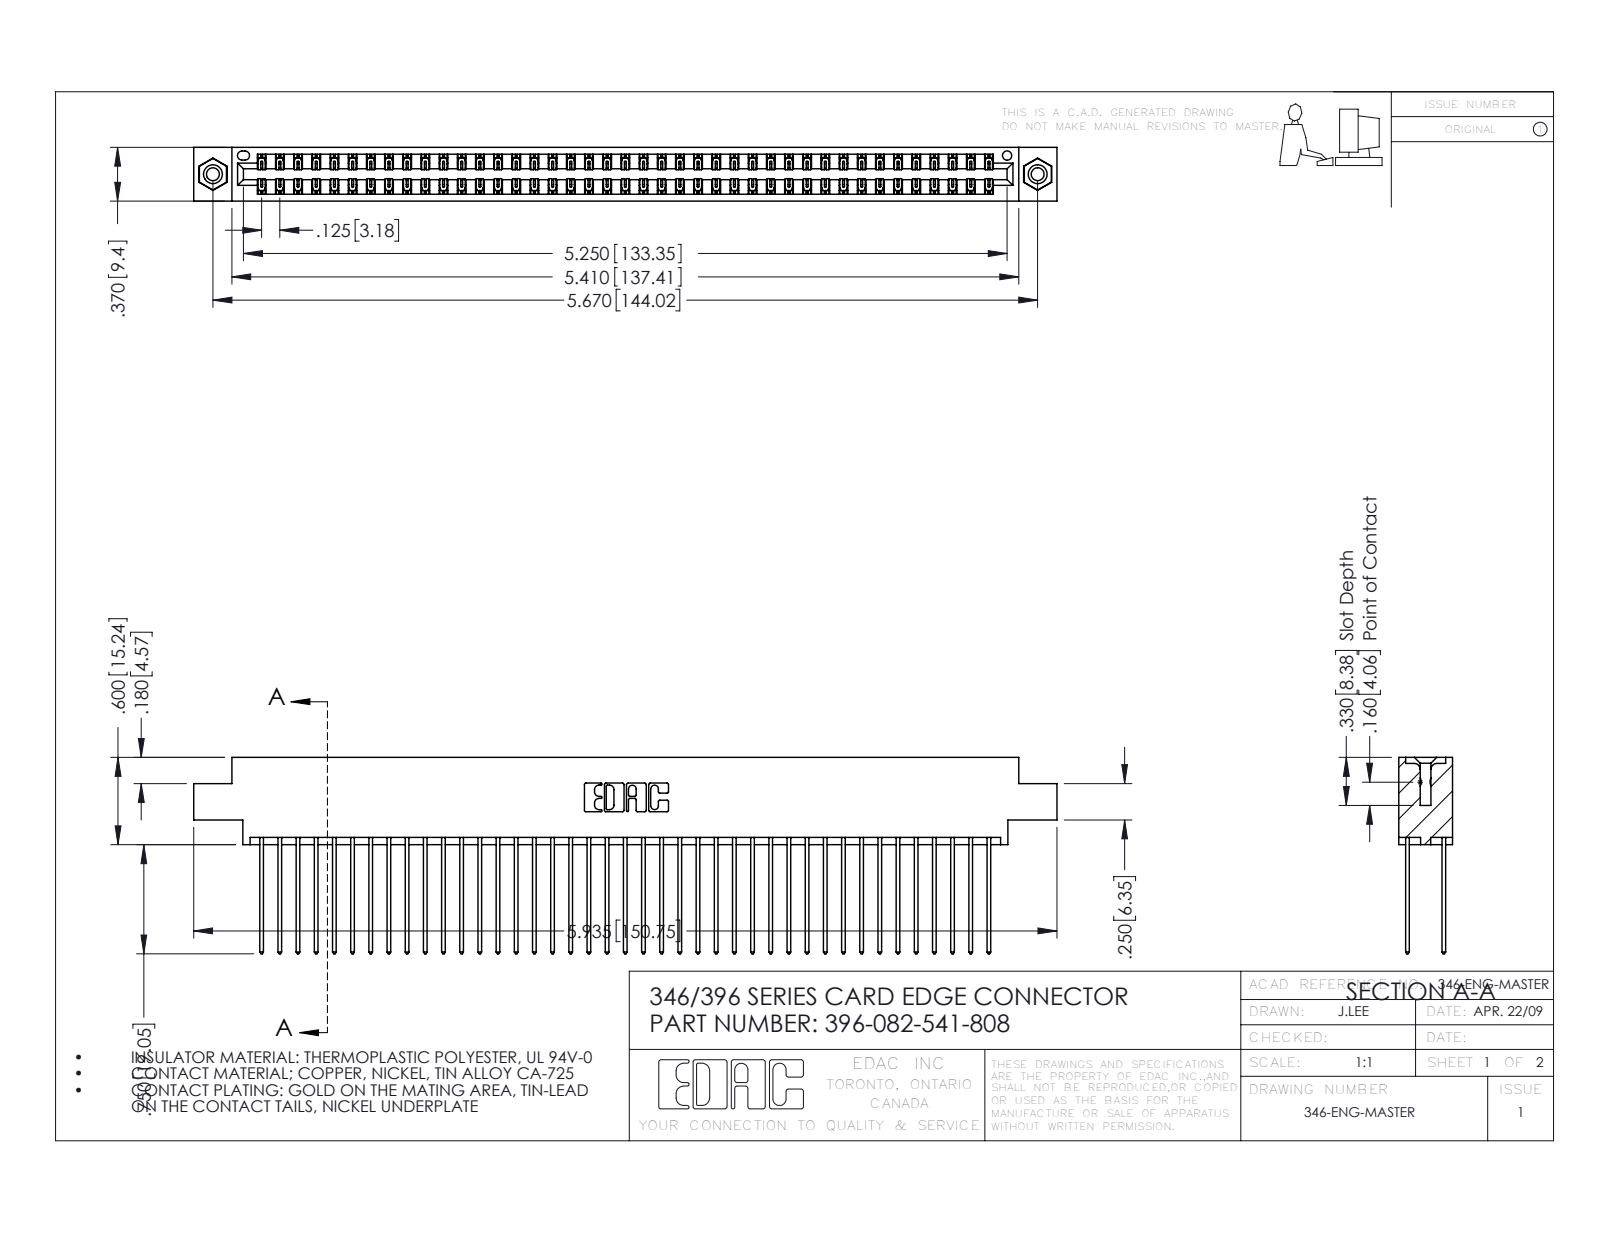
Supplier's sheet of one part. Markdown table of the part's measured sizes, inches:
| quantity | value |
| --- | --- |
| part name | 396-082-541-808; 345-292-001_345-293-141; 345-250-001_345-250-003-102; 346 Part_0.170 Offset - 0.156 Dia-TI |
| STEP written by | SolidWorks 2016 (CONFIG_CONTROL_DESIGN) |
| units | inches |
| bodies | 85 solids, 4450 faces (2982 planar, 1452 cylindrical, 16 other) |
| overall size | 5.935 × 1.35 × 0.37 |
| volume | 0.915 in³ |
| surface area | 35.74 in² |
| round holes (diameter × count) | 0.089 × 2, 0.125 × 2, 0.156 × 2, 0.064 × 1 |
| round bosses / shafts (diameter × count) | 0.155 × 2 |
| partial cylindrical surfaces (radius × count) | 0.006 × 123, 0.01 × 82, 0.01 × 22, 0.007 × 6, 0.031 × 6, 0.026 × 3, 0.014 × 2, 0.022 × 2 |
| main face-to-face distances | 0.048, 0.322, 0.25, 0.072, 0.298, 0.025, 0.37, 0.275, 0.225, 0.222 |
| hole center spacings | 0.246, 5.461, 5.67 |
